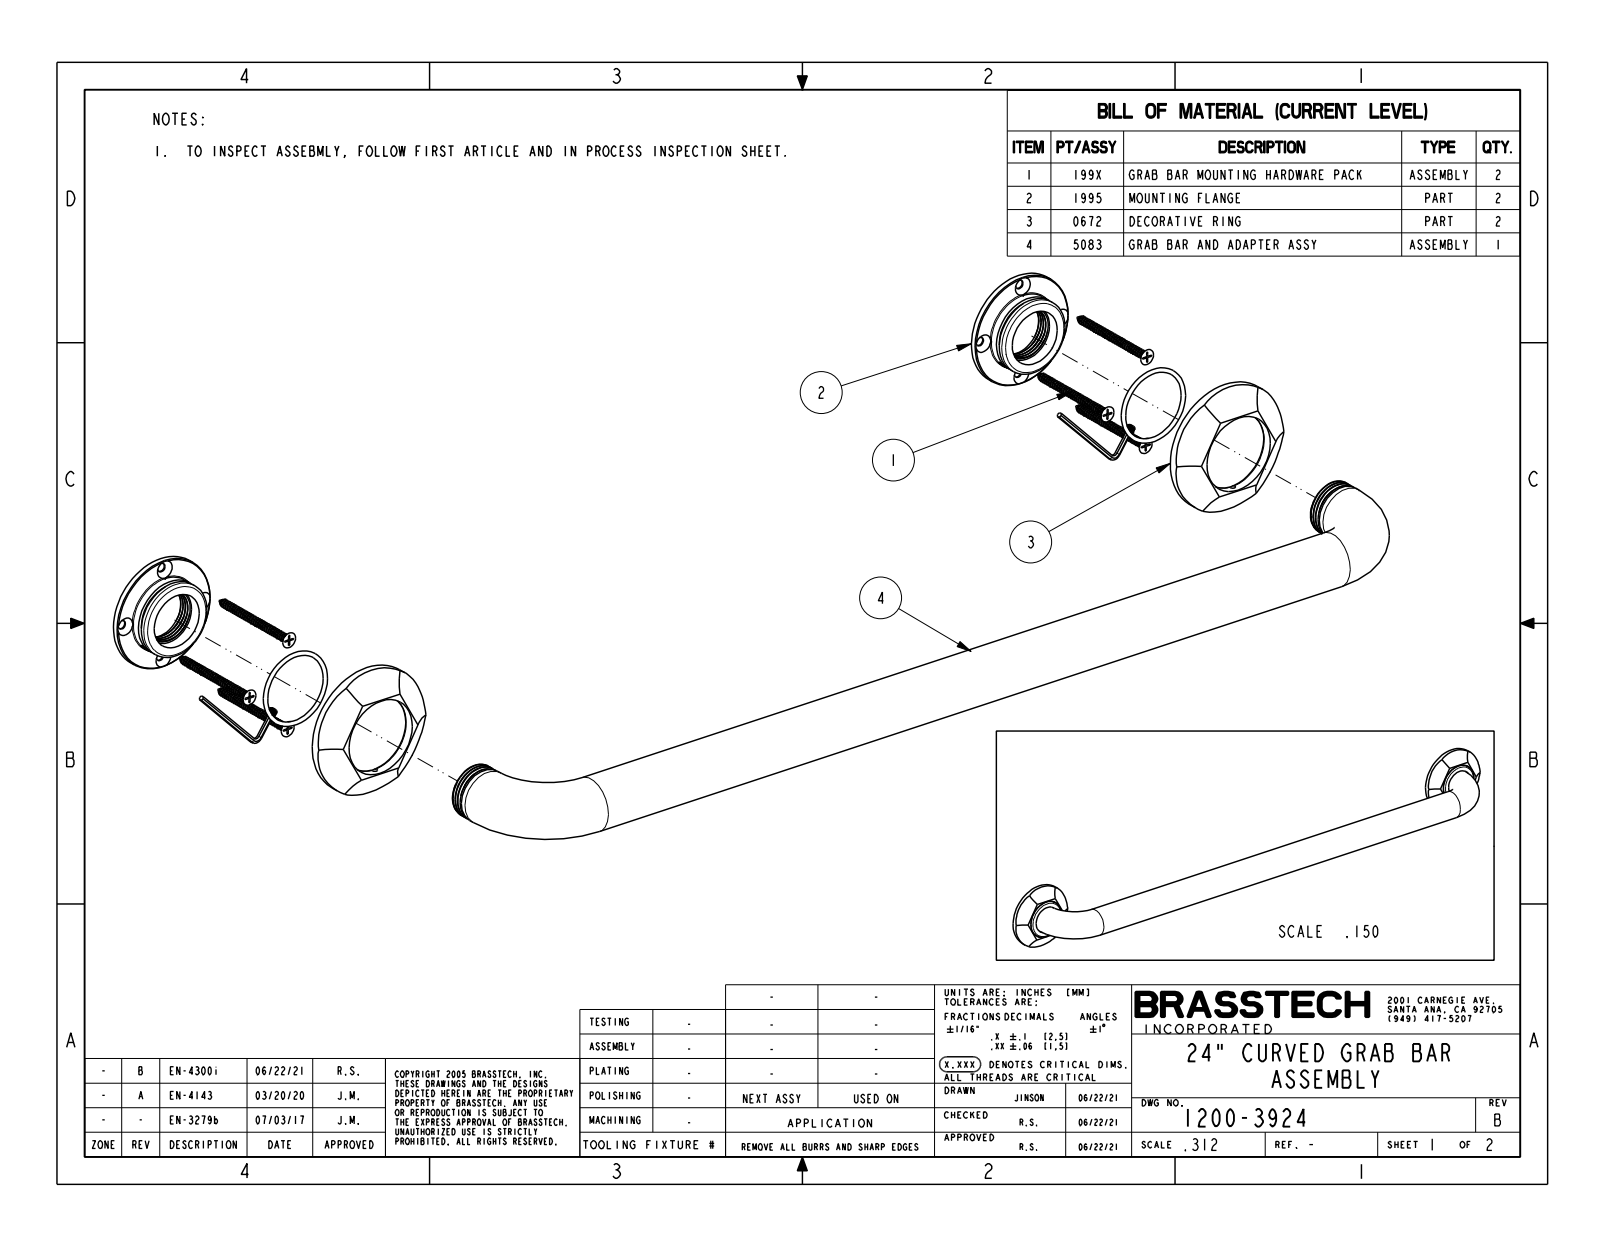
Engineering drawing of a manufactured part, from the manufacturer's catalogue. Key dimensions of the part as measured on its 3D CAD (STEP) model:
Part name (STEP PRODUCT): 1200-3924_SW0001
STEP written by: CREO PARAMETRIC BY PTC INC, 2018400 (CONFIG_CONTROL_DESIGN)
Units: inches
Bodies: 1 solid, 36 faces (6 planar, 22 cylindrical, 8 other)
Overall size (bounding box): 27 × 3 × 2.75
Volume: 37.38 in³ · Surface area: 132.1 in²
Round bosses / shafts (diameter × count): ⌀3 ×2, ⌀1.75 ×2, ⌀1.25 ×1
Partial cylindrical surfaces — rounded edges, fillets, slot ends (radius × count): R1.181 ×10
Main face-to-face distances: 0.6, 0.525, 0.075
